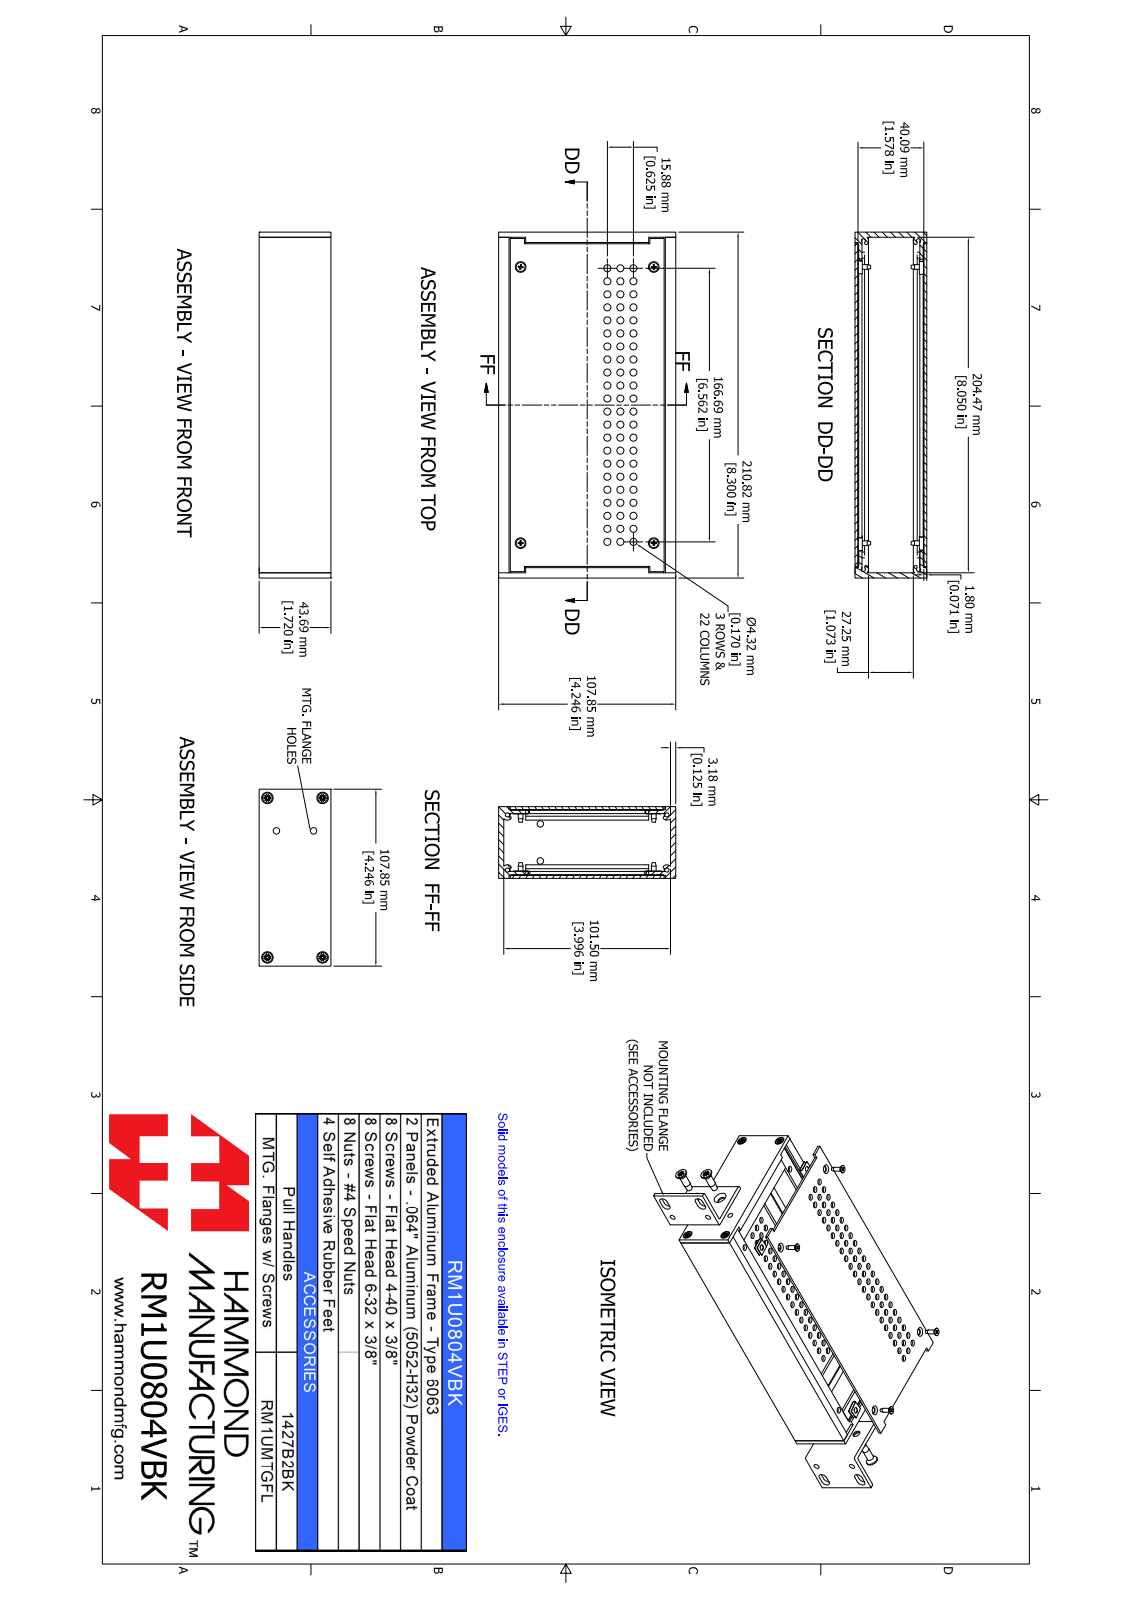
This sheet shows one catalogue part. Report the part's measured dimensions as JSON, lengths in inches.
{"part_name": "RM1U0804VBK", "step_written_by": "SolidWorks 2021 (AUTOMOTIVE_DESIGN)", "units": "inches", "bodies": {"solids": 30, "faces": 936, "planar": 396, "cylindrical": 252, "other": 288}, "overall_size": [8.3, 4.246, 1.72], "volume_in3": 12.2, "surface_area_in2": 277.7, "round_holes": [[0.17, 66], [0.098, 4], [0.138, 4], [0.157, 4], [0.169, 4], [0.156, 2]], "round_bosses_or_shafts": [[0.238, 4], [0.214, 4], [0.138, 4], [0.112, 4]], "partial_cylinders_radius": [[0.039, 8], [0.049, 8], [0.05, 8], [0.125, 8], [0.038, 7], [0.037, 4]], "face_to_face_distances": [0.071, 1.649, 1.72, 1.578, 0.125, 4.121, 1.482, 0.167, 1.553, 0.096], "hole_center_spacings": [0.699, 0.313, 0.625, 0.988, 1.289, 0.442, 0.312, 0.937]}
